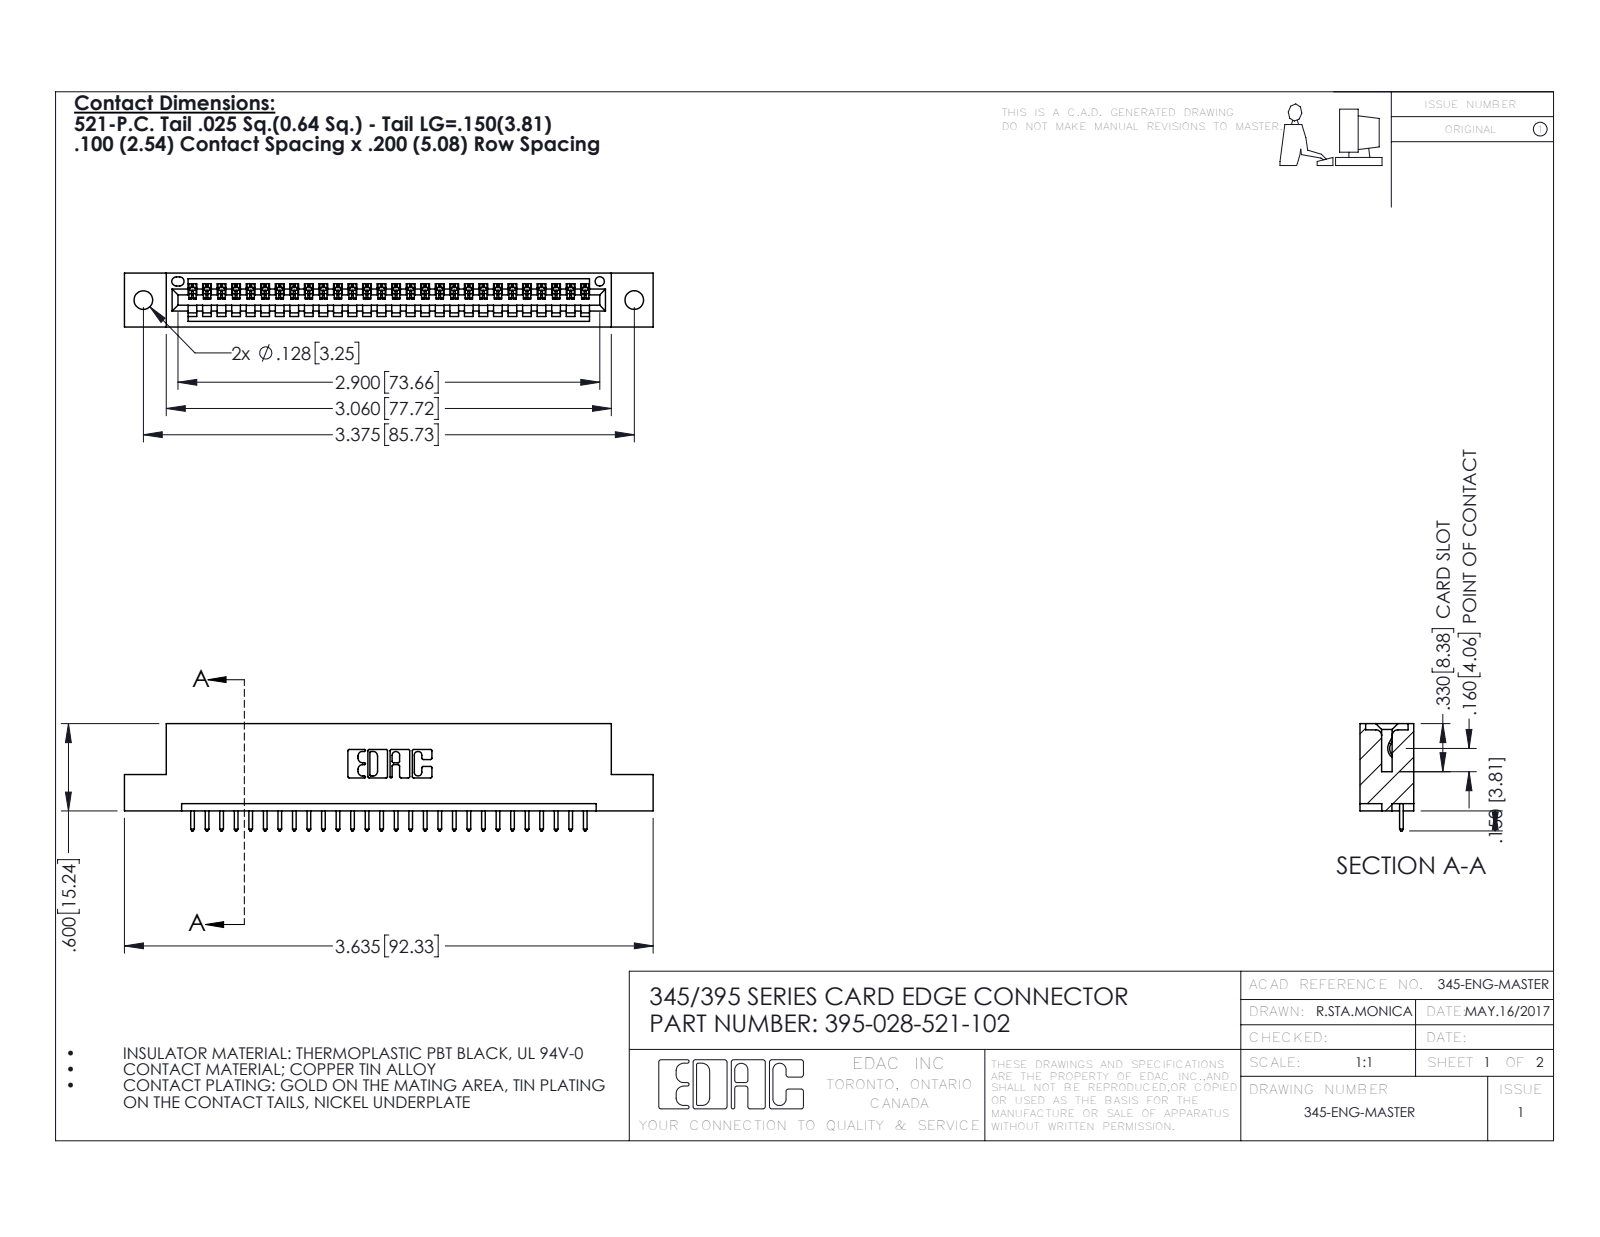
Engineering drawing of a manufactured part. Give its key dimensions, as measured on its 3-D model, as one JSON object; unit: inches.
{"part_name": "395-028-521-102; 345-292-001_345-293-121; 345 Part_Flush Mounting Lugs - 0.128 Dia", "step_written_by": "SolidWorks 2016 (CONFIG_CONTROL_DESIGN)", "units": "inches", "bodies": {"solids": 29, "faces": 1750, "planar": 1200, "cylindrical": 550, "other": 0}, "overall_size": [3.635, 0.737, 0.37], "volume_in3": 0.521, "surface_area_in2": 16.39, "round_holes": [[0.128, 2], [0.064, 1]], "partial_cylinders_radius": [[0.006, 56], [0.01, 56], [0.01, 22], [0.007, 6], [0.031, 6], [0.026, 3], [0.031, 2], [0.04, 2]], "face_to_face_distances": [0.298, 0.072, 0.2, 0.37, 0.098, 0.272, 0.025, 0.225, 0.149, 0.072], "hole_center_spacings": [0.27, 3.14, 3.375]}
